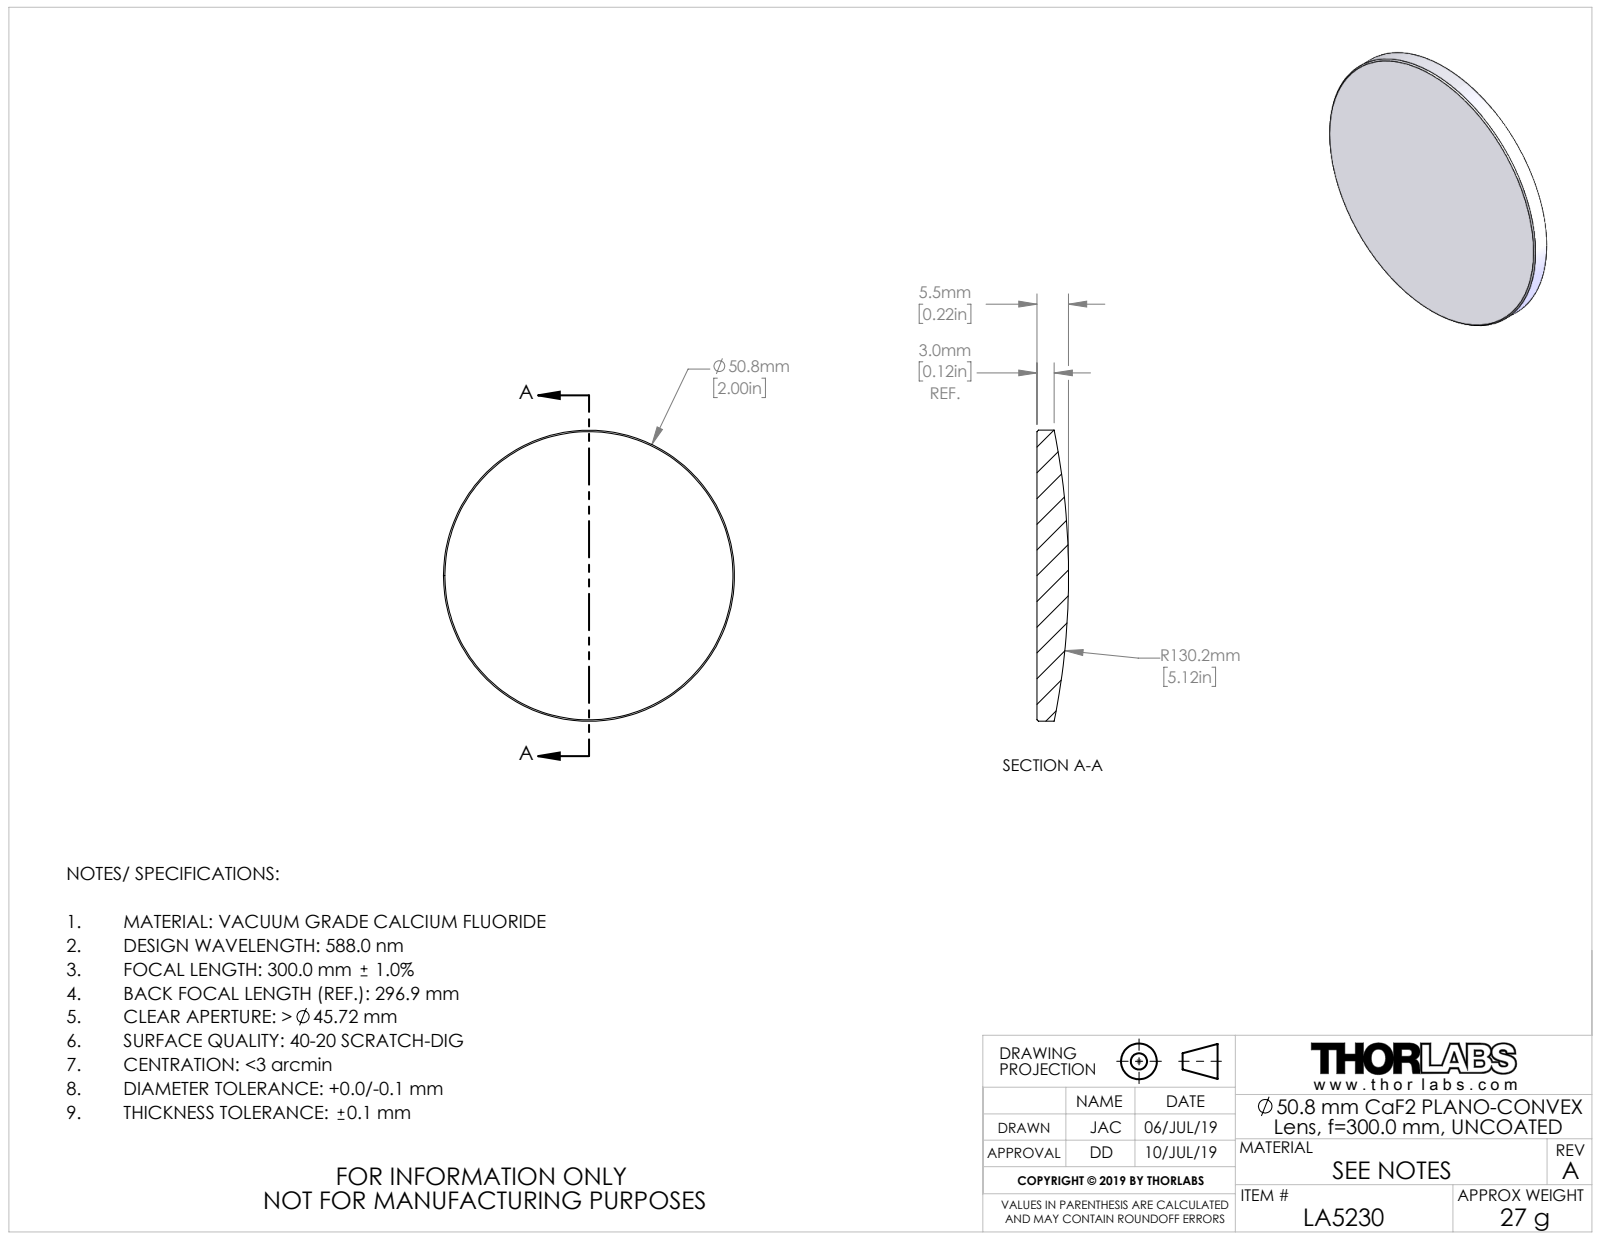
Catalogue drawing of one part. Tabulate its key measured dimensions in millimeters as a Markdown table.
| quantity | value |
| --- | --- |
| part name | TTN188099-E0W |
| STEP written by | SolidWorks 2018 (CONFIG_CONTROL_DESIGN) |
| units | millimeters |
| bodies | 1 solid, 7 faces (1 planar, 2 cylindrical, 4 other) |
| overall size | 50.8 × 50.8 × 5.5 |
| volume | 8 615 mm³ |
| surface area | 4 528 mm² |
| round bosses / shafts (diameter × count) | 50.8 × 1 |
